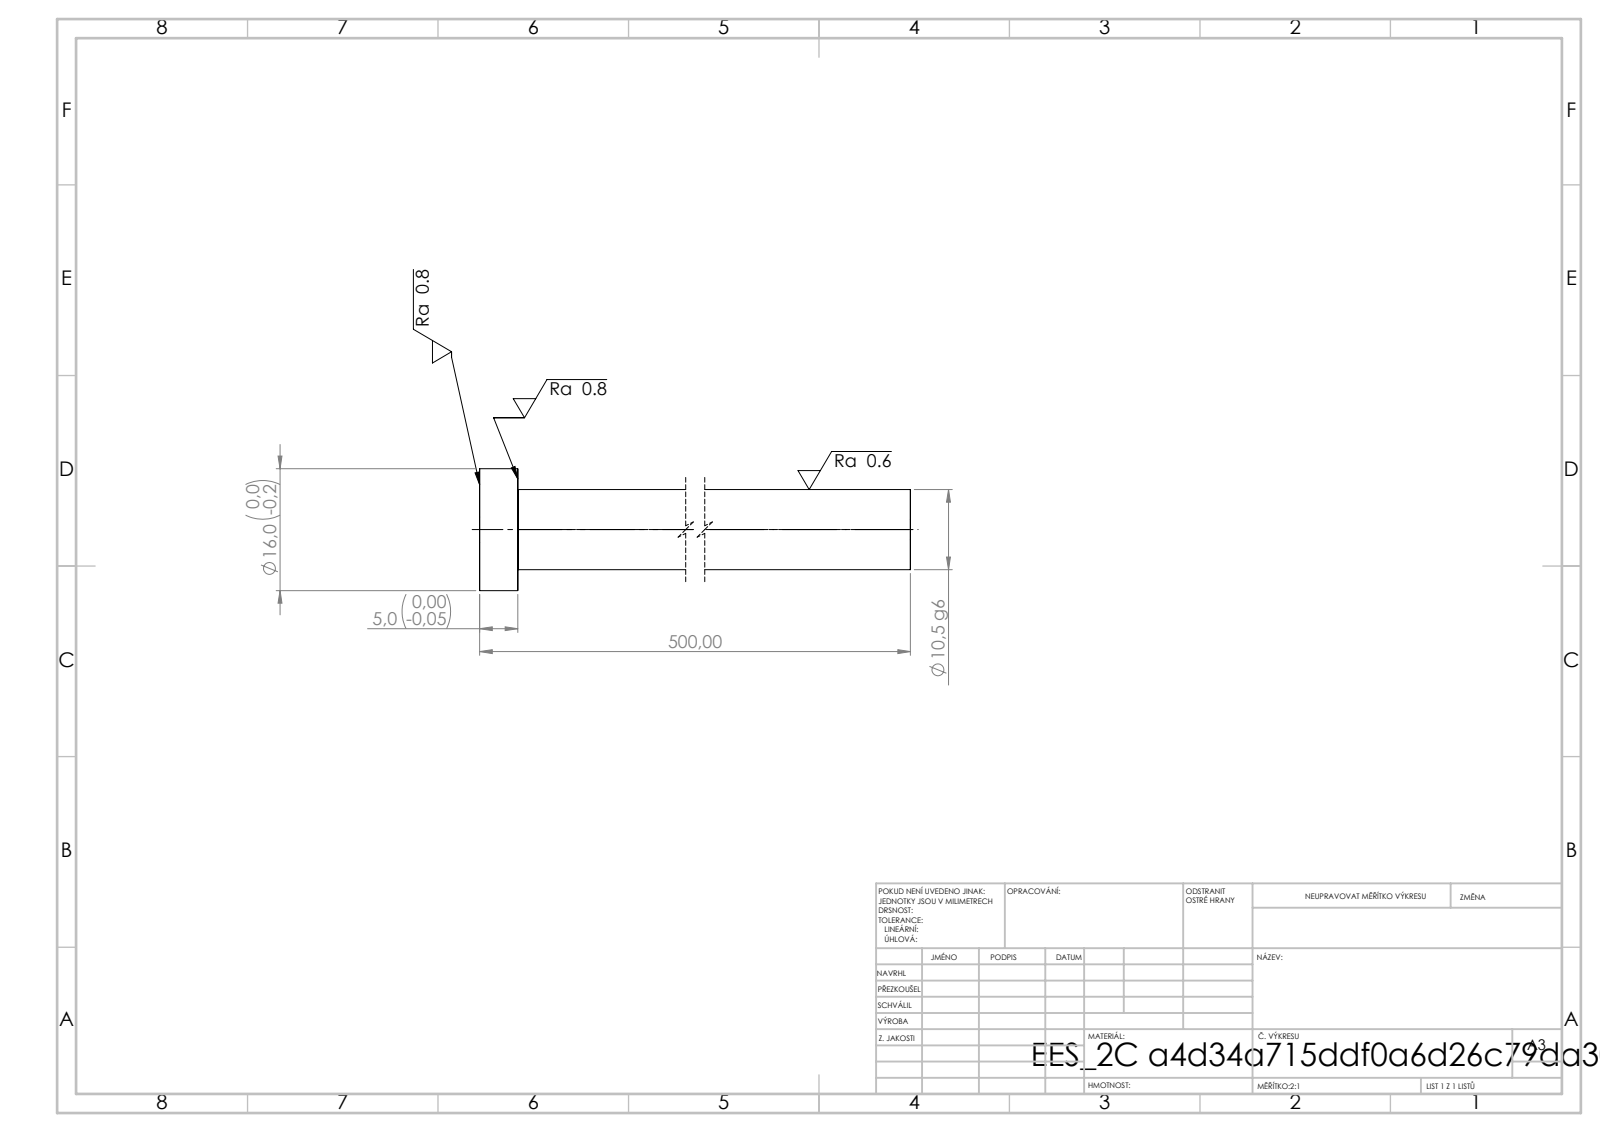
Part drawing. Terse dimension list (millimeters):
written by: SolidWorks 2019 (CONFIG_CONTROL_DESIGN)
unit: mm
bodies: 1 solid, 7 faces (3 planar, 4 cylindrical, 0 other)
size: 500 × 16 × 16
volume: 43 867 mm³; area: 16 982 mm²
bosses: 1× ⌀16, 1× ⌀10.5
face distances: 5, 500, 495
